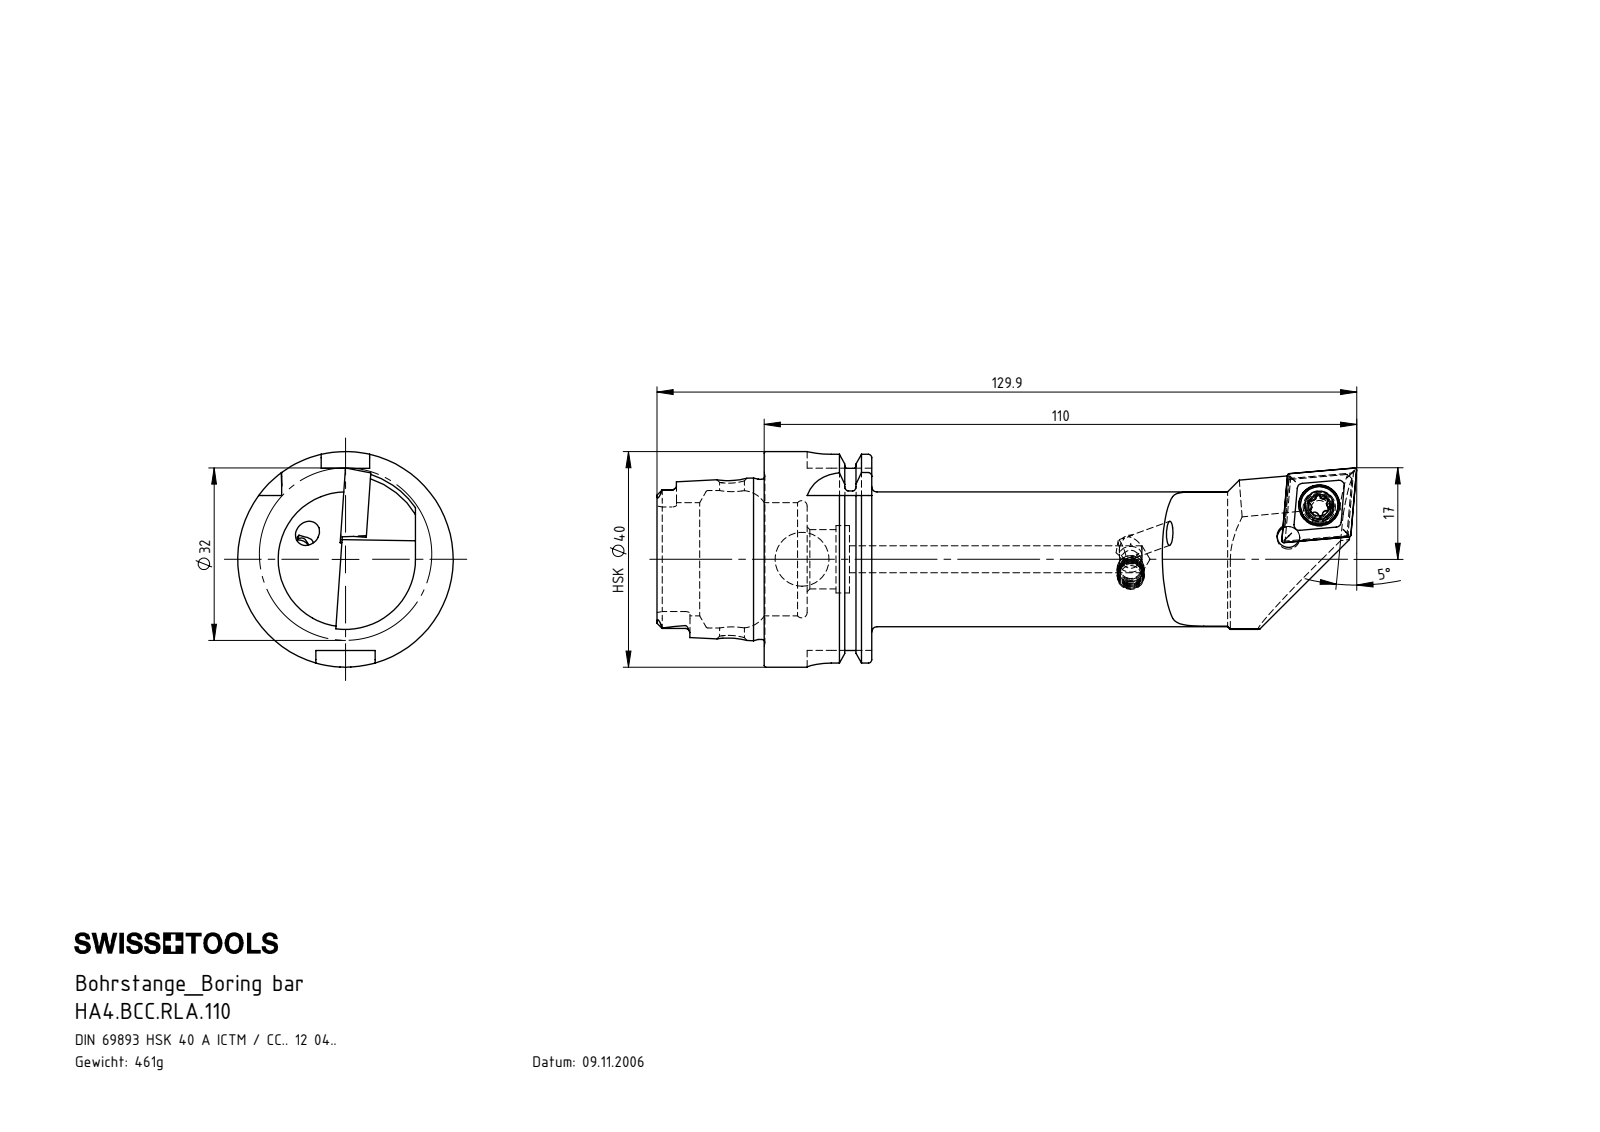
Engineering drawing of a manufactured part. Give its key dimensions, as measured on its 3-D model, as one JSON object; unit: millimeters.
{"part_name": "HA4-BCC.RLA.110_B; WCC-ER2.001.010_A; HA4.BCC.RLA.110; CCMT120404 (+1 more)", "step_written_by": "SolidWorks 2017 (AUTOMOTIVE_DESIGN)", "units": "millimeters", "bodies": {"solids": 5, "faces": 310, "planar": 73, "cylindrical": 95, "other": 142}, "overall_size": [129.86, 40, 40], "volume_mm3": 59857, "surface_area_mm2": 18315, "round_holes": [[4.2, 4], [5, 2], [4, 1], [4.6, 1], [5.5, 1], [7.6, 1], [10, 1], [11, 1], [12.5, 1], [21, 1], [25.5, 1]], "round_bosses_or_shafts": [[5, 2], [40, 1], [34.75, 1], [29.71, 1], [25, 1], [7, 1]], "partial_cylinders_radius": [[0.39, 6], [0.9, 6], [0.69, 3], [0.69, 3], [4.5, 3], [1.82, 2], [1.88, 2], [3, 1]], "face_to_face_distances": [19.95, 4.45, 7.95, 12, 19.9, 27.85, 39.85, 35.7, 15.8, 7.85], "hole_center_spacings": [8.09]}
